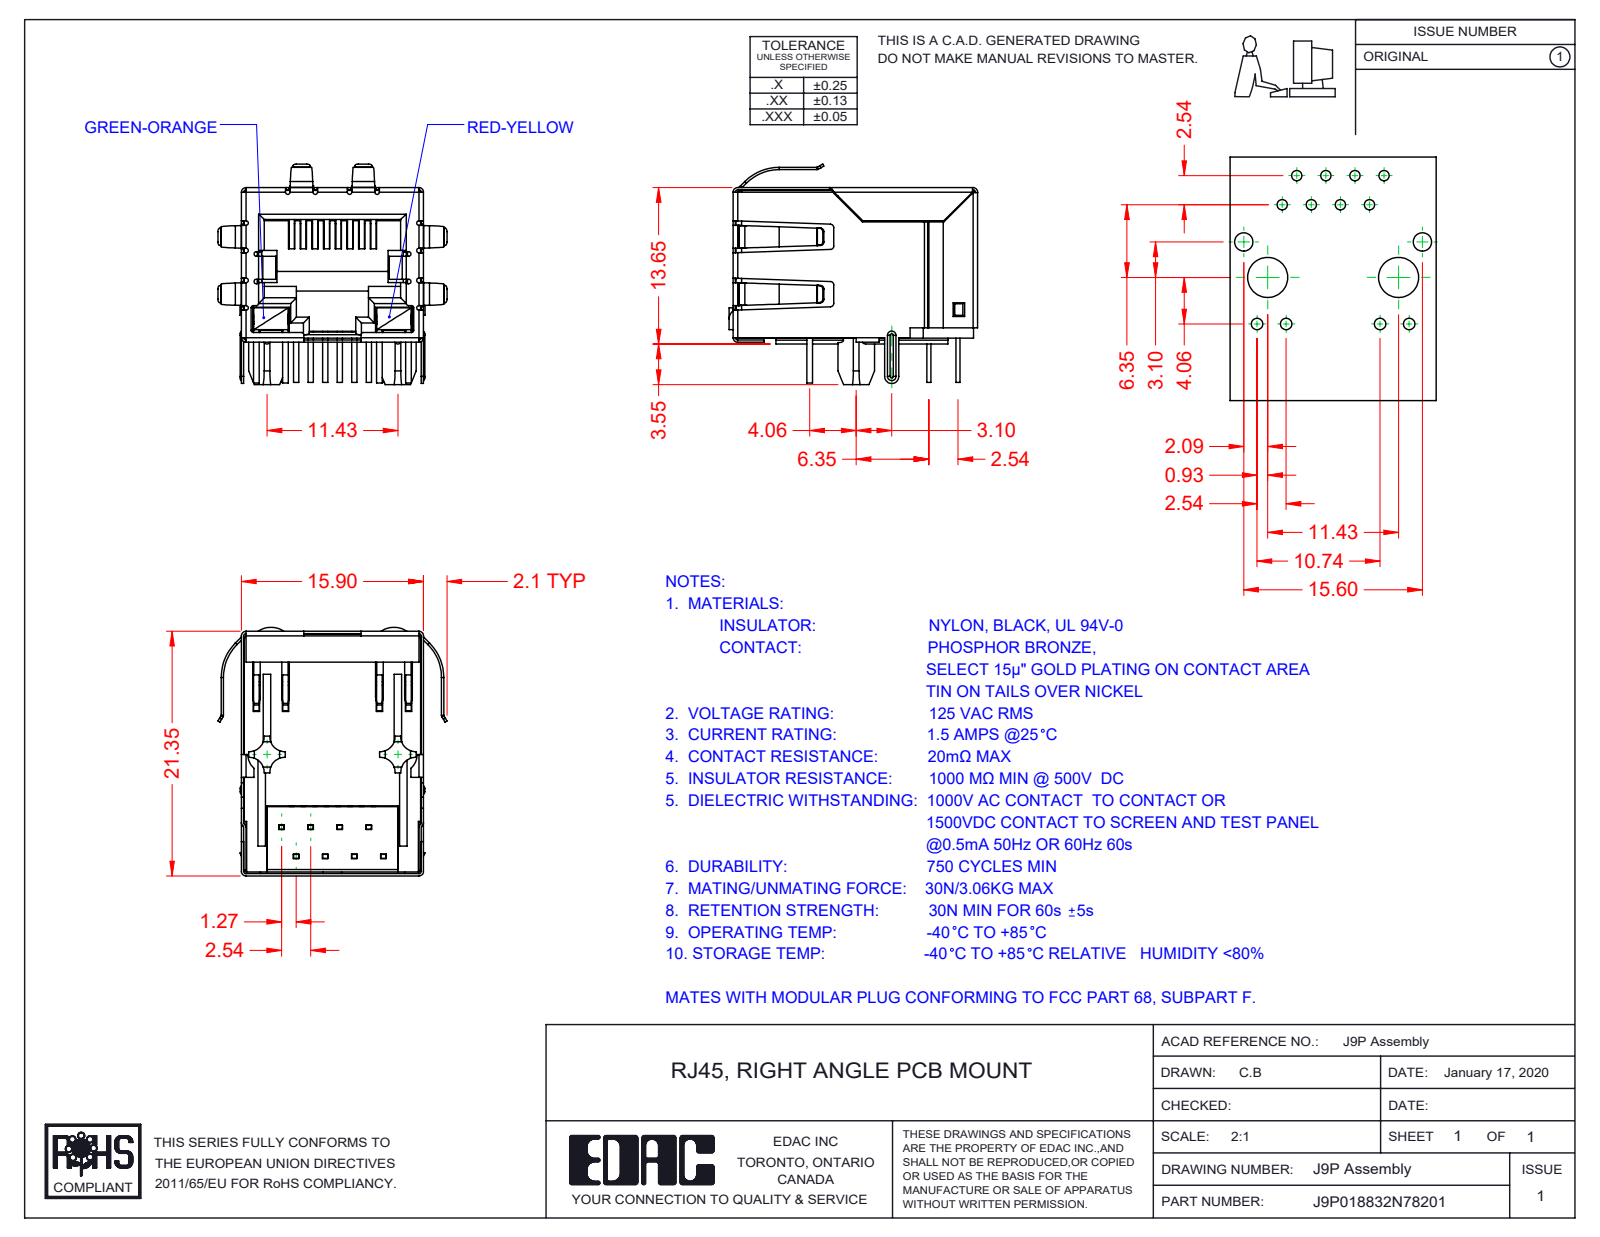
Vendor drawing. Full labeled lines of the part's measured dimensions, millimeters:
Part name (STEP PRODUCT): 9P-LED LED LH_7-Green-Orange; 9P-LED Assembly; 9P-LED Contacts; 9P-LED Shield (+4 more)
STEP written by: SolidWorks 2016 (CONFIG_CONTROL_DESIGN)
Units: millimetres
Bodies: 13 solids, 1476 faces (1042 planar, 340 cylindrical, 94 other)
Overall size (bounding box): 21.7 × 20 × 19.25
Volume: 2 687 mm³ · Surface area: 7 515 mm²
Partial cylindrical surfaces — rounded edges, fillets, slot ends (radius × count): R0.2 ×39, R0.5 ×22, R0.3 ×20, R0.4 ×16, R1.3 ×8, R0.23 ×5, R0.11 ×4, R0.31 ×4
Main face-to-face distances: 15.45, 15.7, 15.65, 0.35, 0.54, 15.5, 12.36, 0.6, 1.4, 0.59
